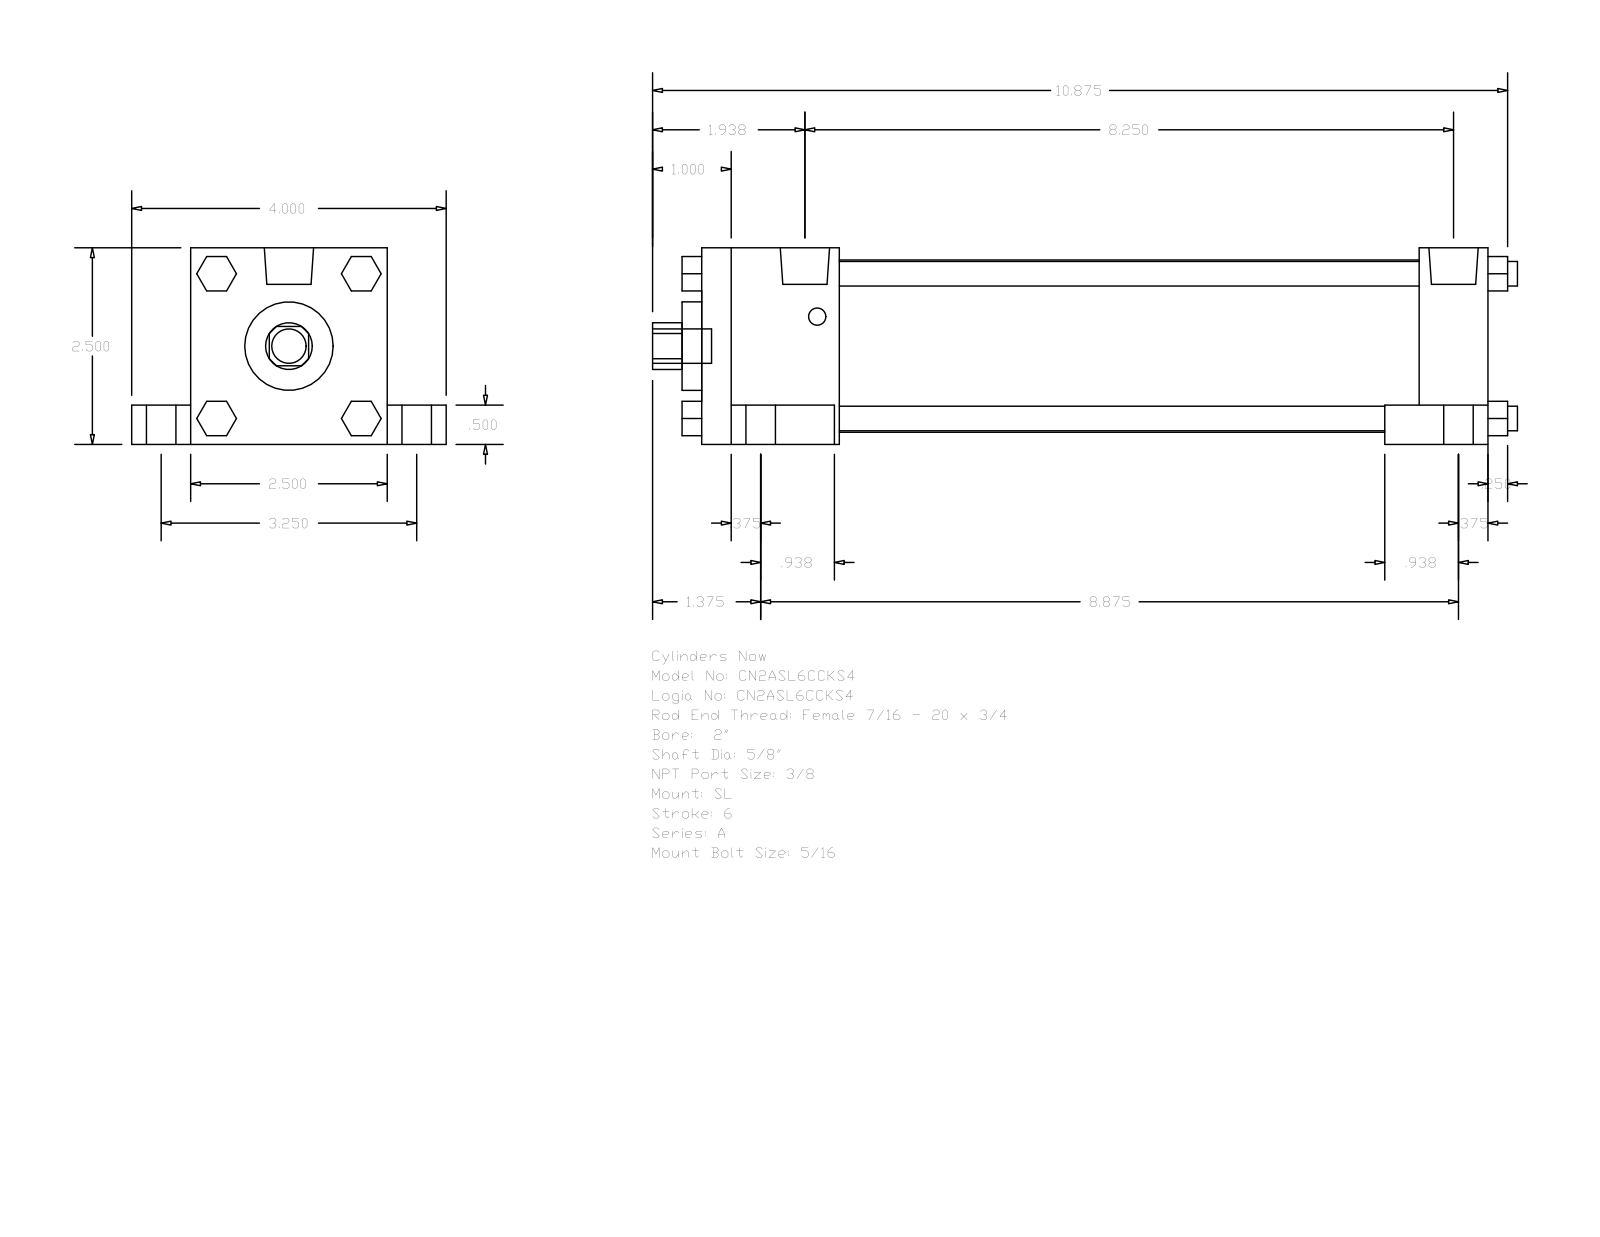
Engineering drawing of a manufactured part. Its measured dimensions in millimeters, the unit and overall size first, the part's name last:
Units: millimetres
Overall size (bounding box): 279.4 × 101.6 × 63.5
Round holes (diameter × count): ⌀15.88 ×1, ⌀28.57 ×1, ⌀55.63 ×1
Round bosses / shafts (diameter × count): ⌀15.88 ×4, ⌀9.53 ×4, ⌀7.94 ×4, ⌀5.56 ×4, ⌀15.93 ×2, ⌀11.11 ×1
Partial cylindrical surfaces — rounded edges, fillets, slot ends (radius × count): R7.54 ×1
Main face-to-face distances: 63.5, 254, 50.8, 12.7, 19.05, 82.55, 44.45, 209.55, 231.77, 187.32
Bodies: 0 solids, 148 faces (112 planar, 36 cylindrical, 0 other)
Part name (STEP PRODUCT): A_SL__0200_0.625
STEP written by: GSSL Pune (CONFIG_CONTROL_DESIGN)
